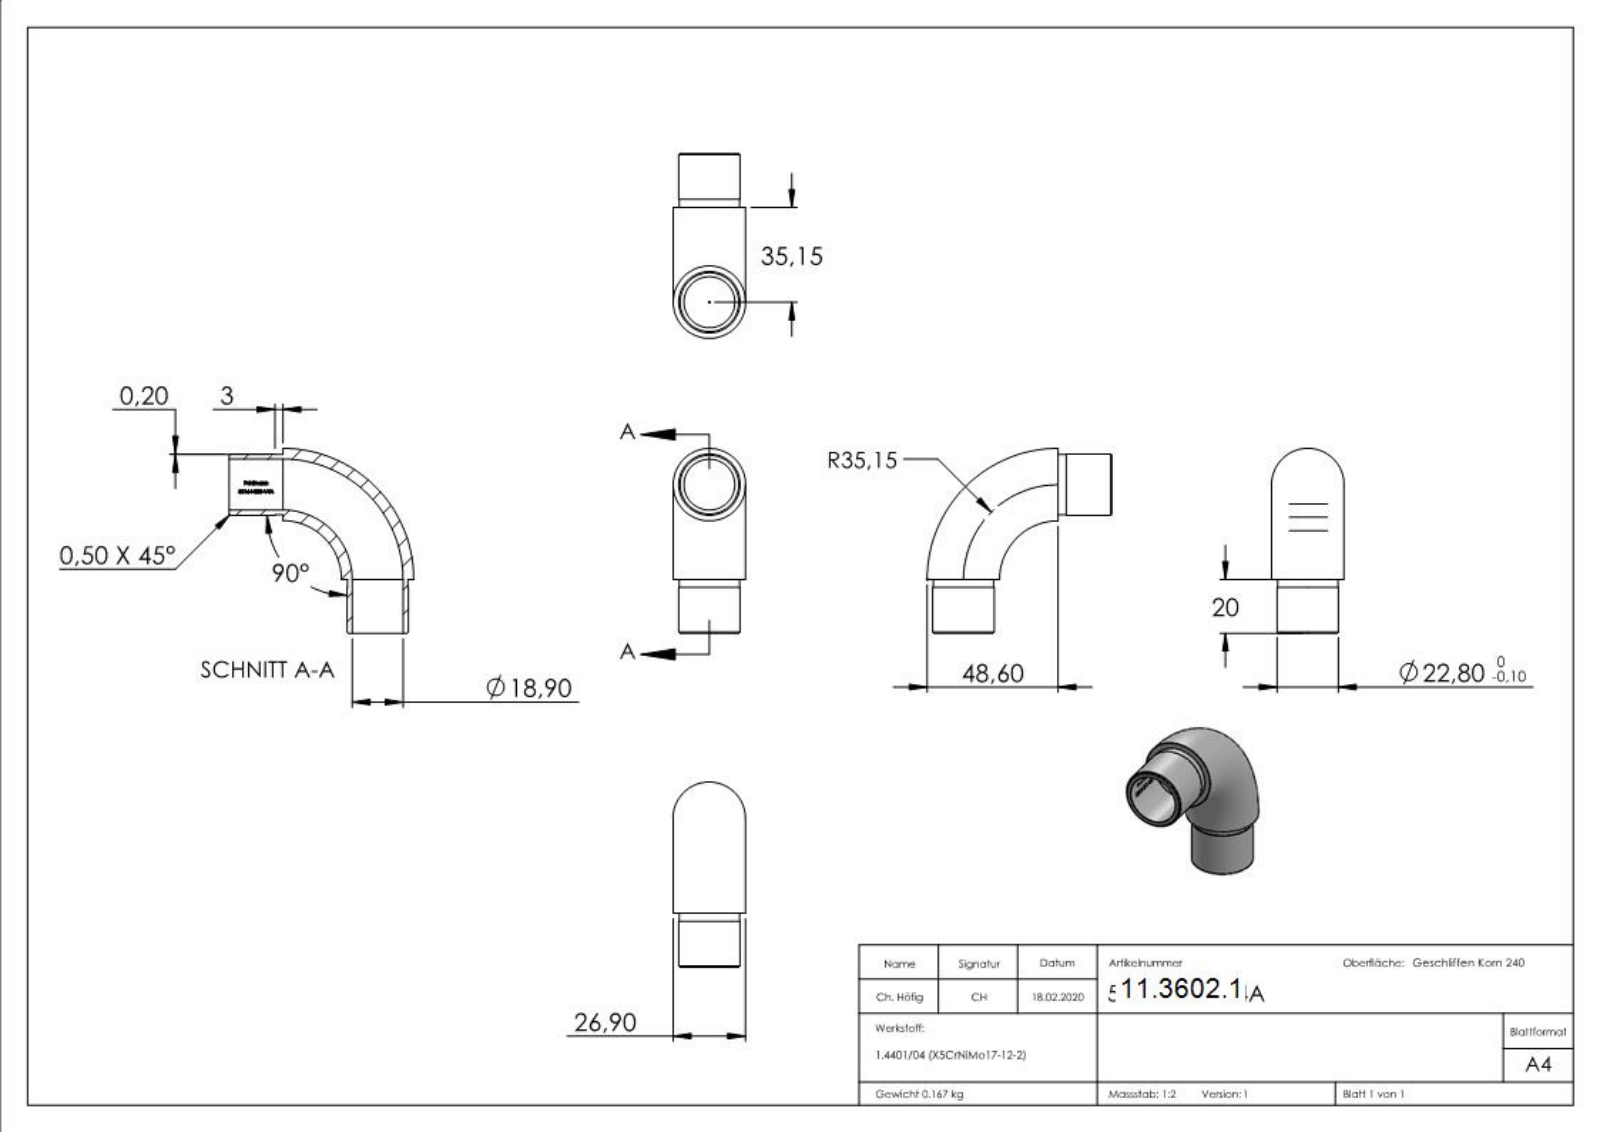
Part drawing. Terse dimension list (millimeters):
name: 56164-320-V4A
written by: SolidWorks 2015 (CONFIG_CONTROL_DESIGN)
unit: mm
bodies: 1 solid, 282 faces (139 planar, 36 cylindrical, 107 other)
size: 68.6 × 68.6 × 26.9
volume: 20 894 mm³; area: 13 778 mm²
holes: 2× ⌀18.9
bosses: 2× ⌀22.8, 2× ⌀22.4
rounds: 1× R9.55
face distances: 20, 17, 3, 5.41, 0.88, 1.32, 0.76, 0.61, 3.66, 3.27
